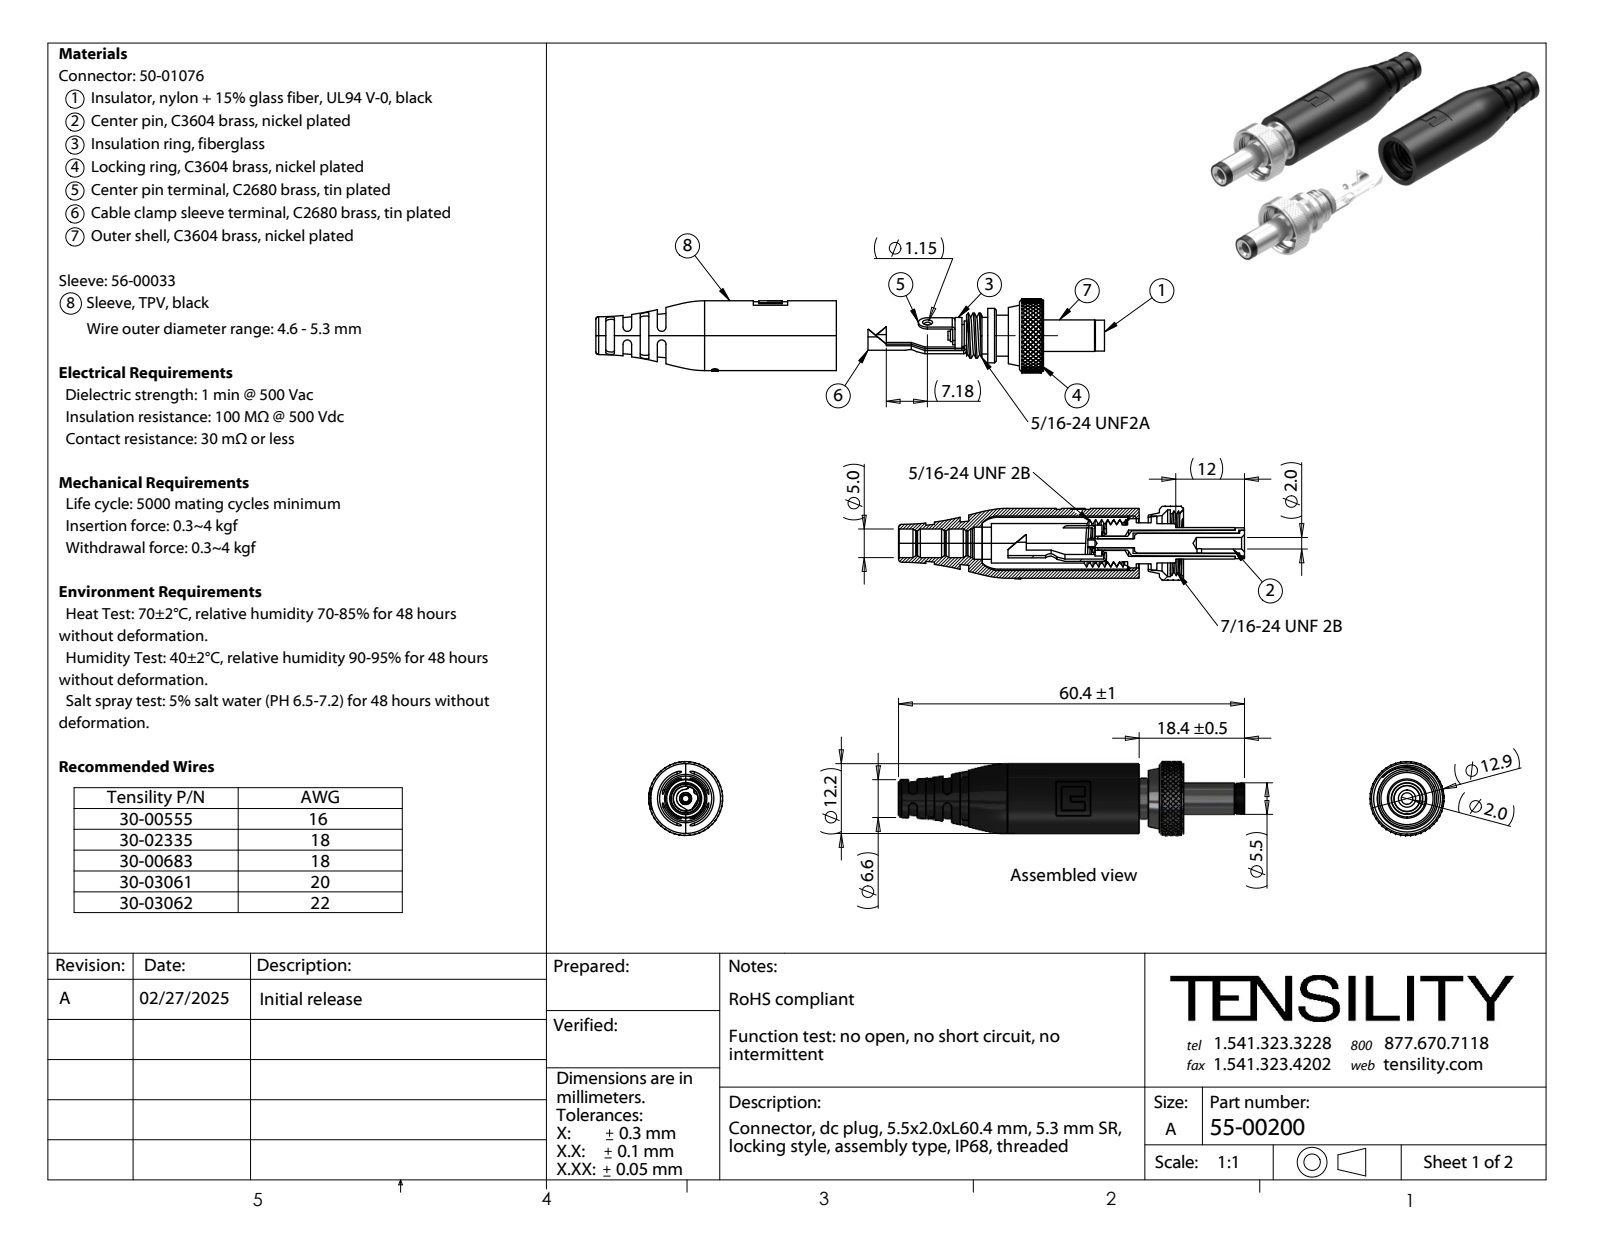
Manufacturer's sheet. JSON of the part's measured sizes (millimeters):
{"part_name": "50-01076_Cable clamp sleeve terminal; 5.0(4.6-5.3); jiaoke; 50-01076_Center pin terminal (+8 more)", "step_written_by": "SolidWorks 2021 (CONFIG_CONTROL_DESIGN)", "units": "millimeters", "bodies": {"solids": 9, "faces": 400, "planar": 128, "cylindrical": 146, "other": 126}, "overall_size": [60.9, 12.9, 12.9], "volume_mm3": 3436, "surface_area_mm2": 7101, "round_holes": [[1.15, 2], [0.8, 1], [1.6, 1], [2, 1], [2.01, 1], [2.45, 1], [2.5, 1], [3.35, 1], [3.55, 1], [4.55, 1], [4.6, 1], [5.6, 1]], "round_bosses_or_shafts": [[12.9, 1], [12.4, 1], [12.2, 1], [7.85, 1], [7.15, 1], [6.85, 1], [6.4, 1], [5.5, 1]], "partial_cylinders_radius": [[0.75, 8], [0.2, 4], [1.57, 2], [6.1, 2], [0.1, 1], [0.4, 1], [0.5, 1], [0.6, 1]], "face_to_face_distances": [1.5, 29.75, 0.4, 4.3, 5.2, 4.1, 1.6, 3.7, 3.6, 1.7]}
